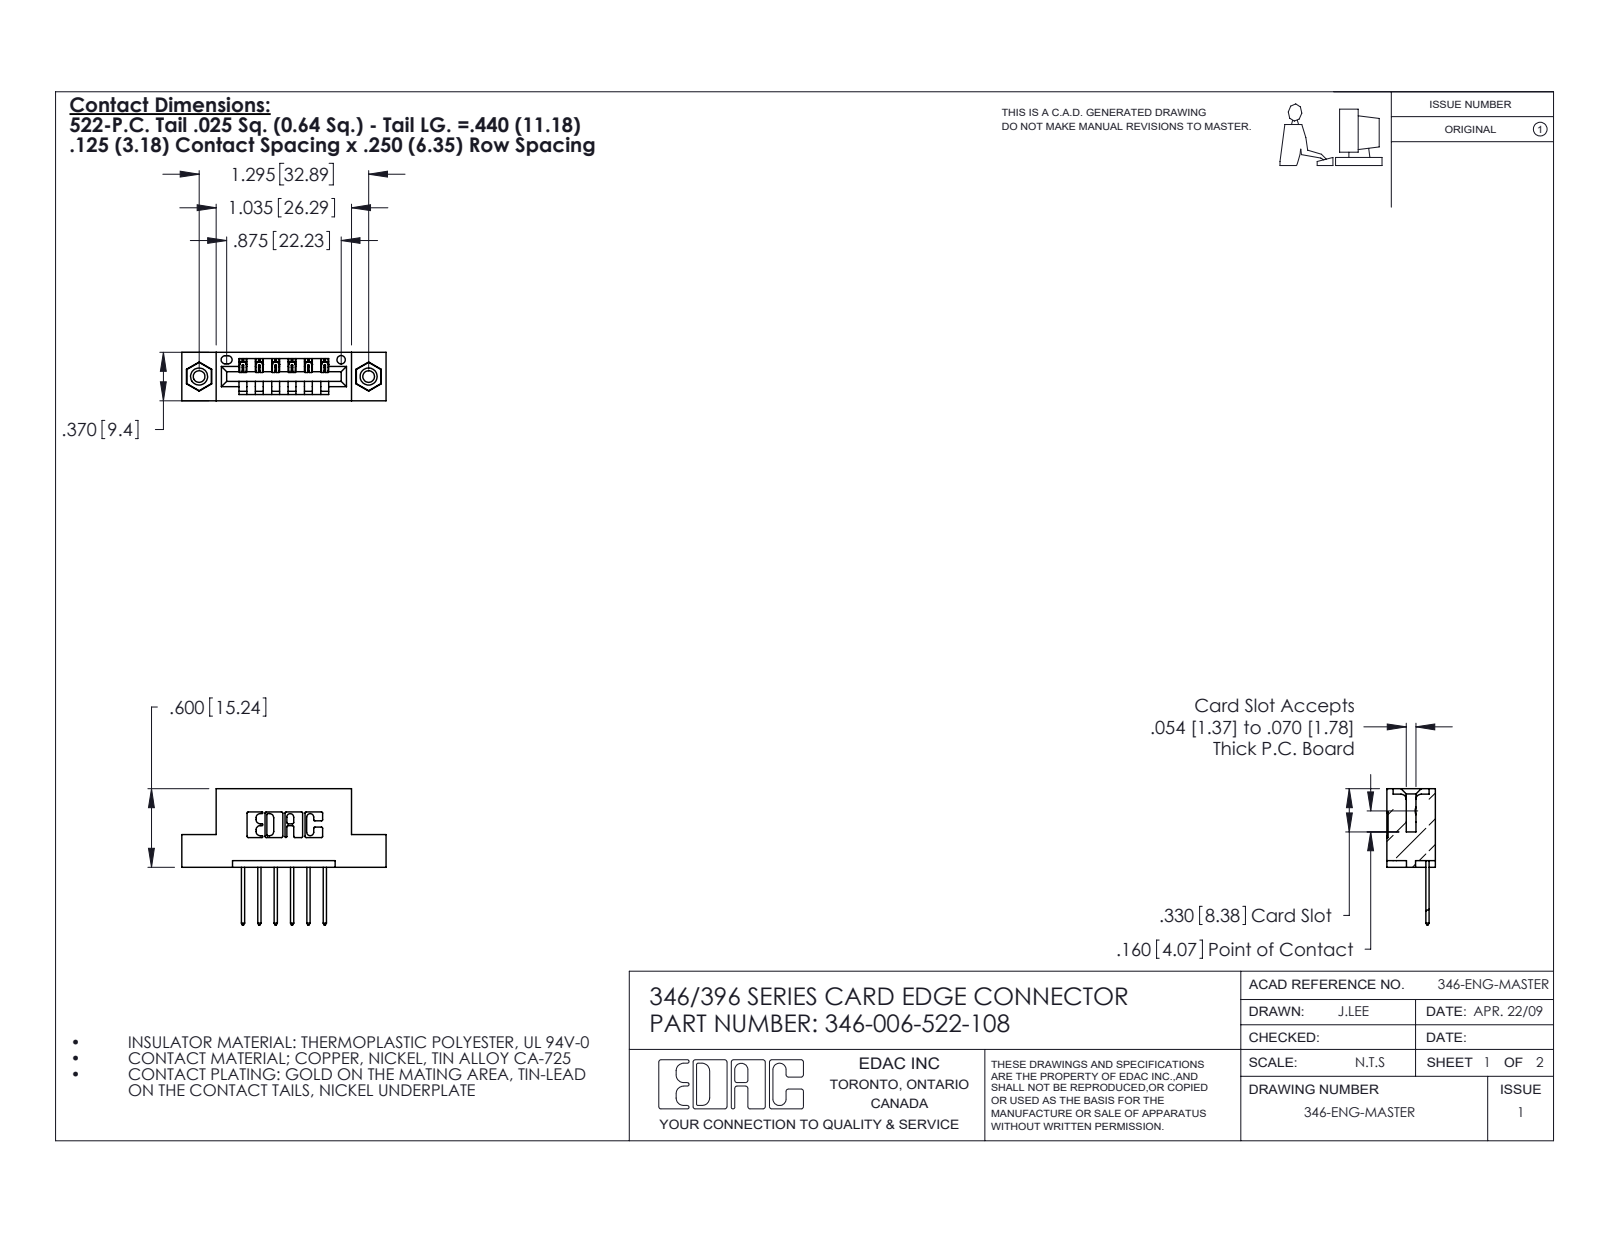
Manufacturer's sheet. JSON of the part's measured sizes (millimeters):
{"part_name": "345-292-001_345-293-122; 346-006-522-108; 345-250-001_345-250-003-102; 346 Part_Flush Mounting Lugs - 0.156 Dia-TI", "step_written_by": "SolidWorks 2020 (CONFIG_CONTROL_DESIGN)", "units": "millimeters", "bodies": {"solids": 9, "faces": 530, "planar": 348, "cylindrical": 166, "other": 16}, "overall_size": [39.6, 26.4, 9.4], "volume_mm3": 3540, "surface_area_mm2": 4079, "round_holes": [[2.3, 2], [3.2, 2], [4, 2], [1.6, 1]], "round_bosses_or_shafts": [[3.9, 2]], "partial_cylinders_radius": [[0.3, 22], [0.2, 12], [0.3, 12], [0.2, 6], [0.8, 6], [0.7, 3], [0.8, 2], [1, 2]], "face_to_face_distances": [6.4, 9.4, 1.2, 8.2, 1.8, 7.6, 0.6, 3.8, 5.6, 2.5], "hole_center_spacings": [6.2, 27.7, 32.9]}
